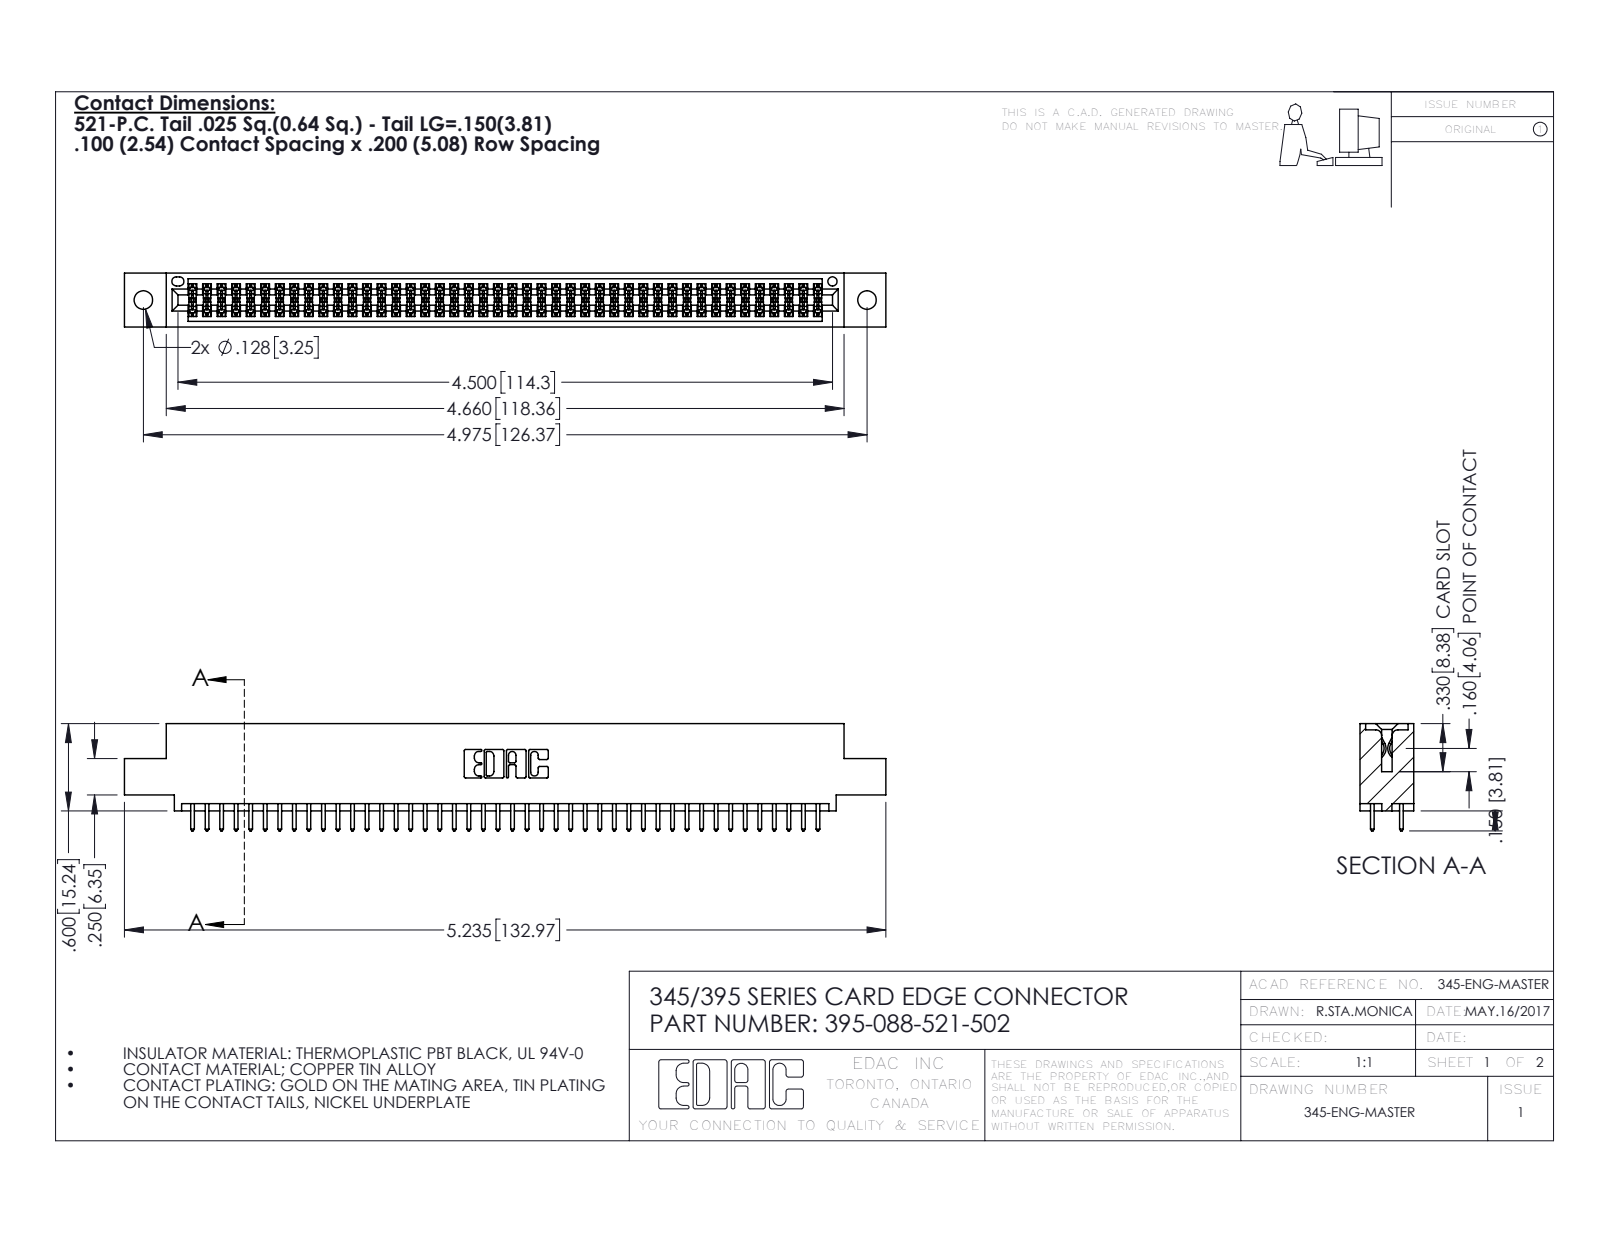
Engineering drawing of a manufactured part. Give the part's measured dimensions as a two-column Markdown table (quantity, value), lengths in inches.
| quantity | value |
| --- | --- |
| part name | 395-088-521-502; 345-292-001_345-293-121; 345 Part_0.110 Offset - 0.128 Dia |
| STEP written by | SolidWorks 2016 (CONFIG_CONTROL_DESIGN) |
| units | inches |
| bodies | 89 solids, 4530 faces (2988 planar, 1542 cylindrical, 0 other) |
| overall size | 5.235 × 0.737 × 0.37 |
| volume | 0.78 in³ |
| surface area | 28.72 in² |
| round holes (diameter × count) | 0.128 × 2, 0.064 × 1 |
| partial cylindrical surfaces (radius × count) | 0.006 × 132, 0.01 × 88, 0.01 × 22, 0.007 × 6, 0.031 × 6, 0.026 × 3, 0.014 × 2, 0.019 × 2 |
| main face-to-face distances | 0.298, 0.072, 0.2, 0.37, 0.098, 0.272, 0.025, 0.225, 0.175, 0.149 |
| hole center spacings | 0.27, 4.739, 4.975 |
